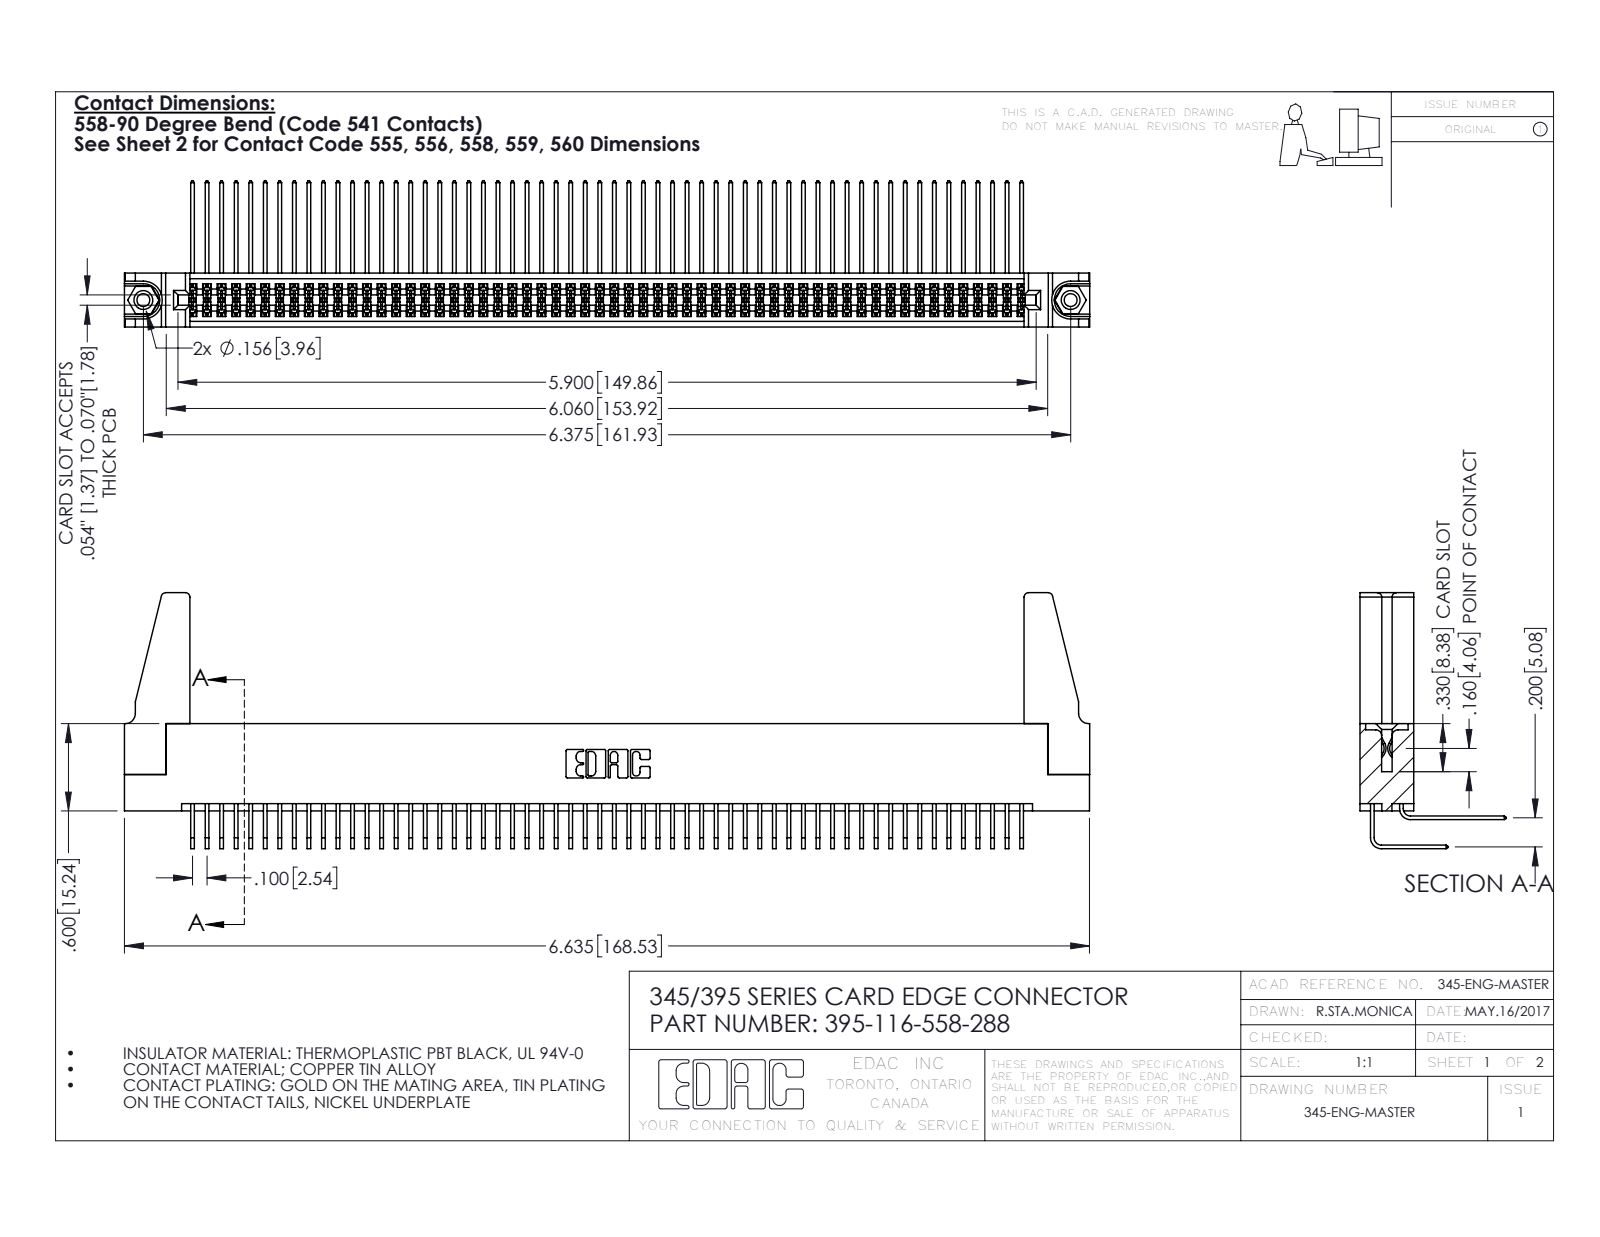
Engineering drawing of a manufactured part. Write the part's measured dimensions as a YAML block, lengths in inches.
part_name: "345 Part_Flush Mounting Lugs - 0.156 Dia-TH; 395-116-558-288; 345-292-001_558 559 Tail - 1; 345-292-001_558 Tail - 2 (+2 more)"
step_written_by: "SolidWorks 2016 (CONFIG_CONTROL_DESIGN)"
units: inches
bodies: {solids: 121, faces: 6282, planar: 4212, cylindrical: 2054, other: 16}
overall_size: [6.636, 1.759, 1.005]
volume: 1.248
surface_area: 49.58
round_holes:
  - {diameter: 0.089, count: 2}
  - {diameter: 0.125, count: 2}
  - {diameter: 0.156, count: 2}
  - {diameter: 0.064, count: 1}
round_bosses_or_shafts:
  - {diameter: 0.155, count: 2}
partial_cylinders:
  - {radius: 0.006, count: 174}
  - {radius: 0.01, count: 22}
  - {radius: 0.03, count: 8}
  - {radius: 0.007, count: 6}
  - {radius: 0.031, count: 6}
  - {radius: 0.026, count: 3}
  - {radius: 0.014, count: 2}
  - {radius: 0.019, count: 2}
face_to_face_distances: [0.072, 0.298, 0.2, 0.37, 0.098, 0.272, 0.025, 0.225, 0.025, 0.285]
hole_center_spacings: [0.27, 6.139, 6.375]
